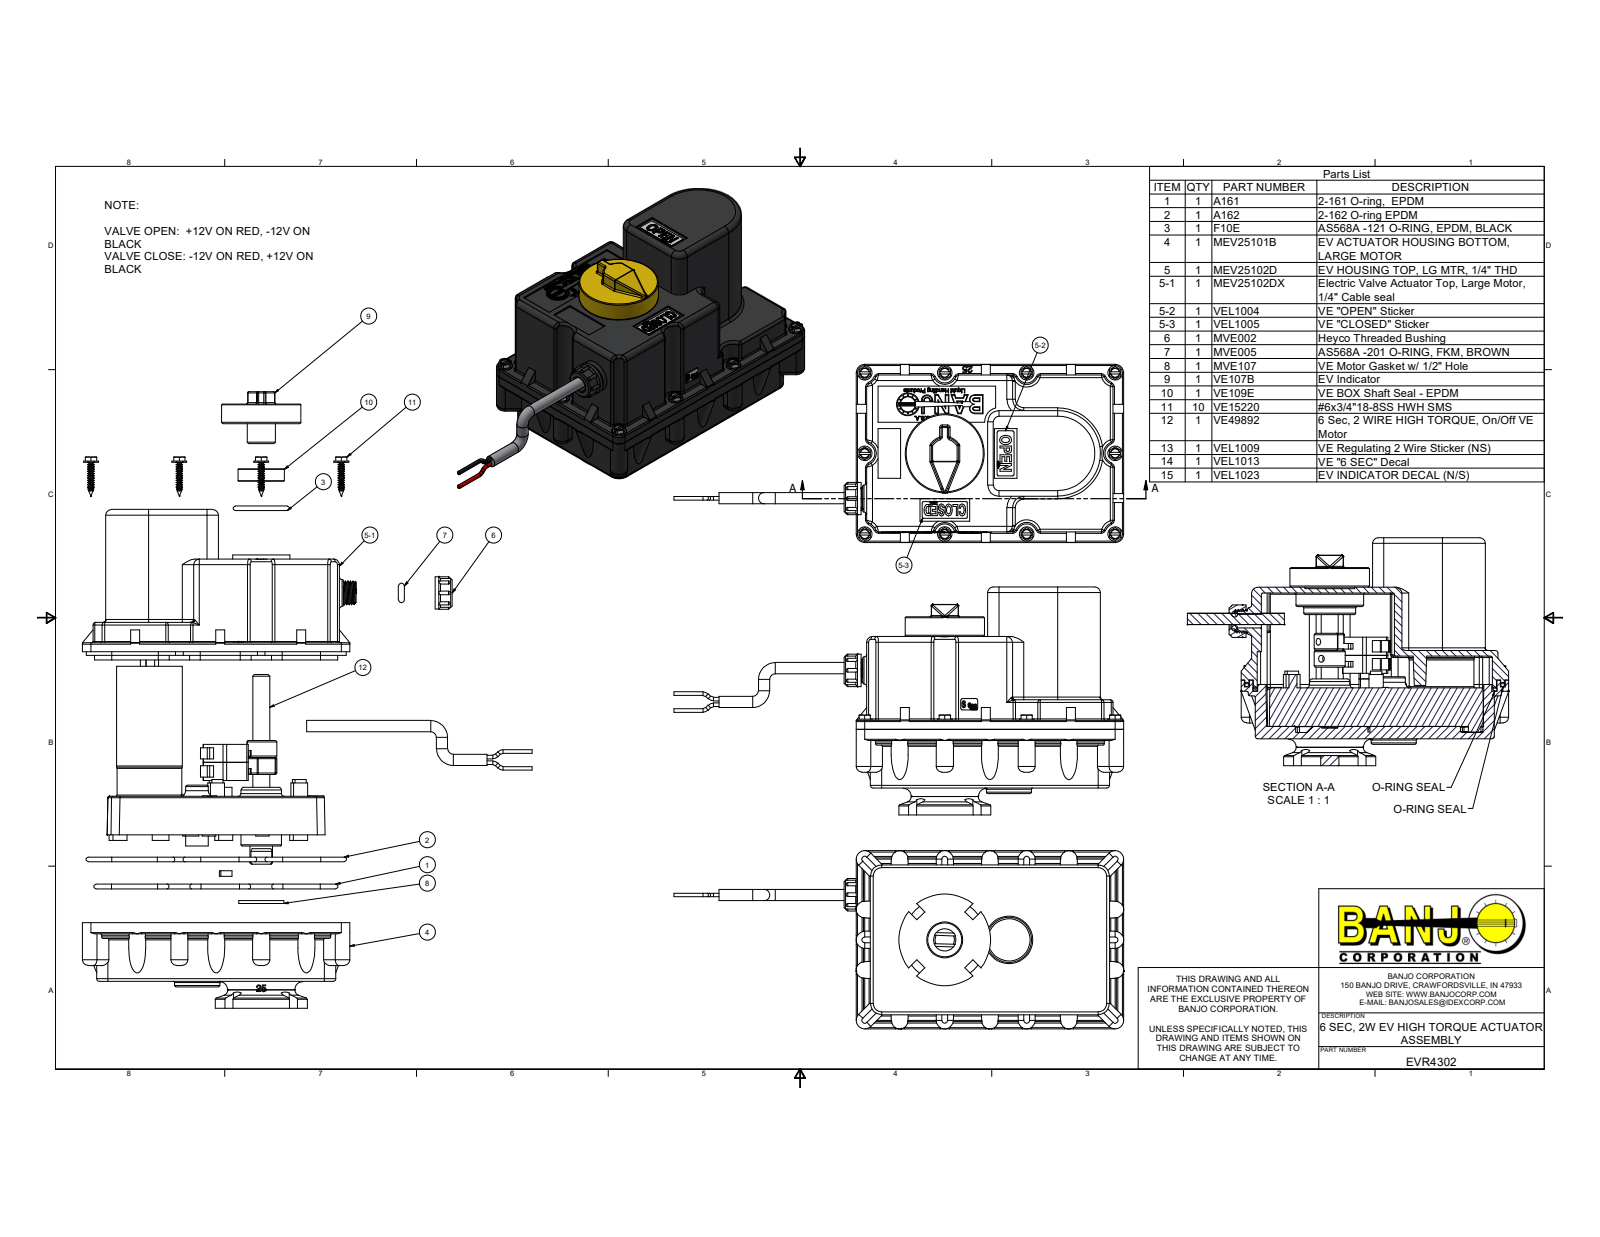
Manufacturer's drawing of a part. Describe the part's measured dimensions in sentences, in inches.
The part is named "EVR4302; MEV25101B; MEV25102D; MEV25102DX (+8 more)". Its 3-D file was written by "Autodesk Inventor 2022 (AUTOMOTIVE_DESIGN)". It is 32 solids with 7933 faces: 3851 planar, 978 cylindrical and 3104 other. Overall it measures 9.971 by 5.055 by 3.95 inches. Its volume is 40.2 cubic inches and its surface area 380.5 square inches. Round holes: 10 of diameter 0.11, 10 of diameter 0.16, 10 of diameter 0.2, 6 of diameter 0.12, 6 of diameter 0.13, 6 of diameter 0.15, 4 of diameter 0.176, 3 of diameter 0.375, 2 of diameter 0.085, 2 of diameter 0.115, 2 of diameter 0.5, 1 of diameter 0.156. Round bosses or shafts: 10 of diameter 0.328, 10 of diameter 0.138, 9 of diameter 0.25, 8 of diameter 0.103, 6 of diameter 0.315, 6 of diameter 0.3, 6 of diameter 0.08, 4 of diameter 0.32. Partial cylindrical surfaces (rounded edges, fillets, slot ends): 93 of radius 0.03, 43 of radius 0.06, 28 of radius 0.125, 27 of radius 0.02, 24 of radius 0.315, 24 of radius 0.5, 16 of radius 0.39, 12 of radius 0.031. The main face-to-face distances are 0.125, 3.355, 0.275, 3.23, 0.045, 0.79, 2.565, 2.955, 0.85, 1.125. The hole center spacings are 1.68, 2.058, 2.376, 1.785, 0.348, 0.492, 1.188, 1.265.
